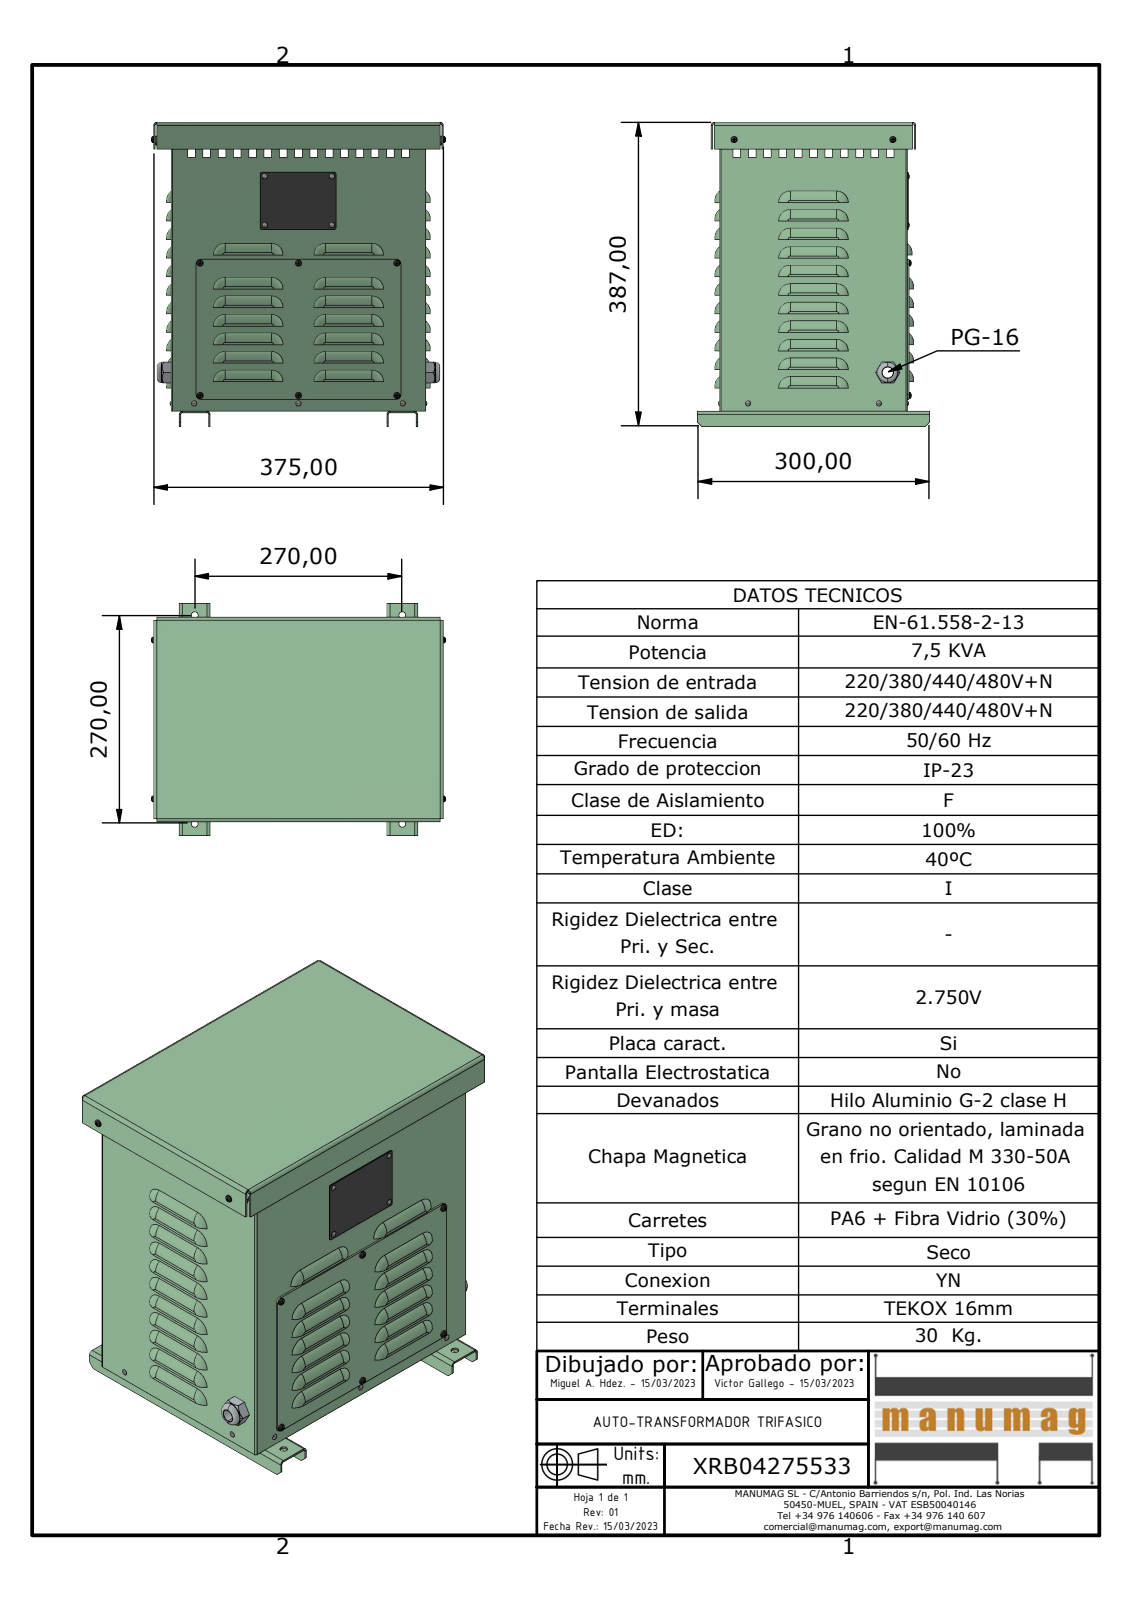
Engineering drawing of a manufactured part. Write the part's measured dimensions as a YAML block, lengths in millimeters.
part_name: "XRB04275533; JE010 EXPORT BASE; JE010 EXPORT PATA; JE010 EXPORT CUERPO (+6 more)"
step_written_by: "Autodesk Inventor 2023 (AUTOMOTIVE_DESIGN)"
units: millimeters
bodies: {solids: 33, faces: 1975, planar: 1082, cylindrical: 421, other: 472}
overall_size: [394.02, 381.14, 300]
volume: 1720000
surface_area: 1517000
round_holes:
  - {diameter: 2.3, count: 8}
  - {diameter: 3.7, count: 8}
  - {diameter: 8.8, count: 8}
  - {diameter: 4.3, count: 5}
  - {diameter: 3.4, count: 4}
  - {diameter: 4, count: 4}
  - {diameter: 5, count: 3}
  - {diameter: 14, count: 1}
  - {diameter: 24, count: 1}
round_bosses_or_shafts:
  - {diameter: 3.2, count: 9}
  - {diameter: 4, count: 8}
  - {diameter: 3.62, count: 8}
  - {diameter: 26, count: 1}
  - {diameter: 23, count: 1}
  - {diameter: 22.5, count: 1}
partial_cylinders:
  - {radius: 14, count: 105}
  - {radius: 4, count: 68}
  - {radius: 15, count: 40}
  - {radius: 2, count: 20}
  - {radius: 1.5, count: 6}
  - {radius: 2, count: 5}
  - {radius: 6, count: 4}
face_to_face_distances: [2, 240.62, 327.32, 372.01, 242.62, 374.01, 238.62, 325.32, 329.32, 4]
hole_center_spacings: [55.99, 127.3, 168.89, 210.03, 213.21, 213.3, 342.86, 62.98]
